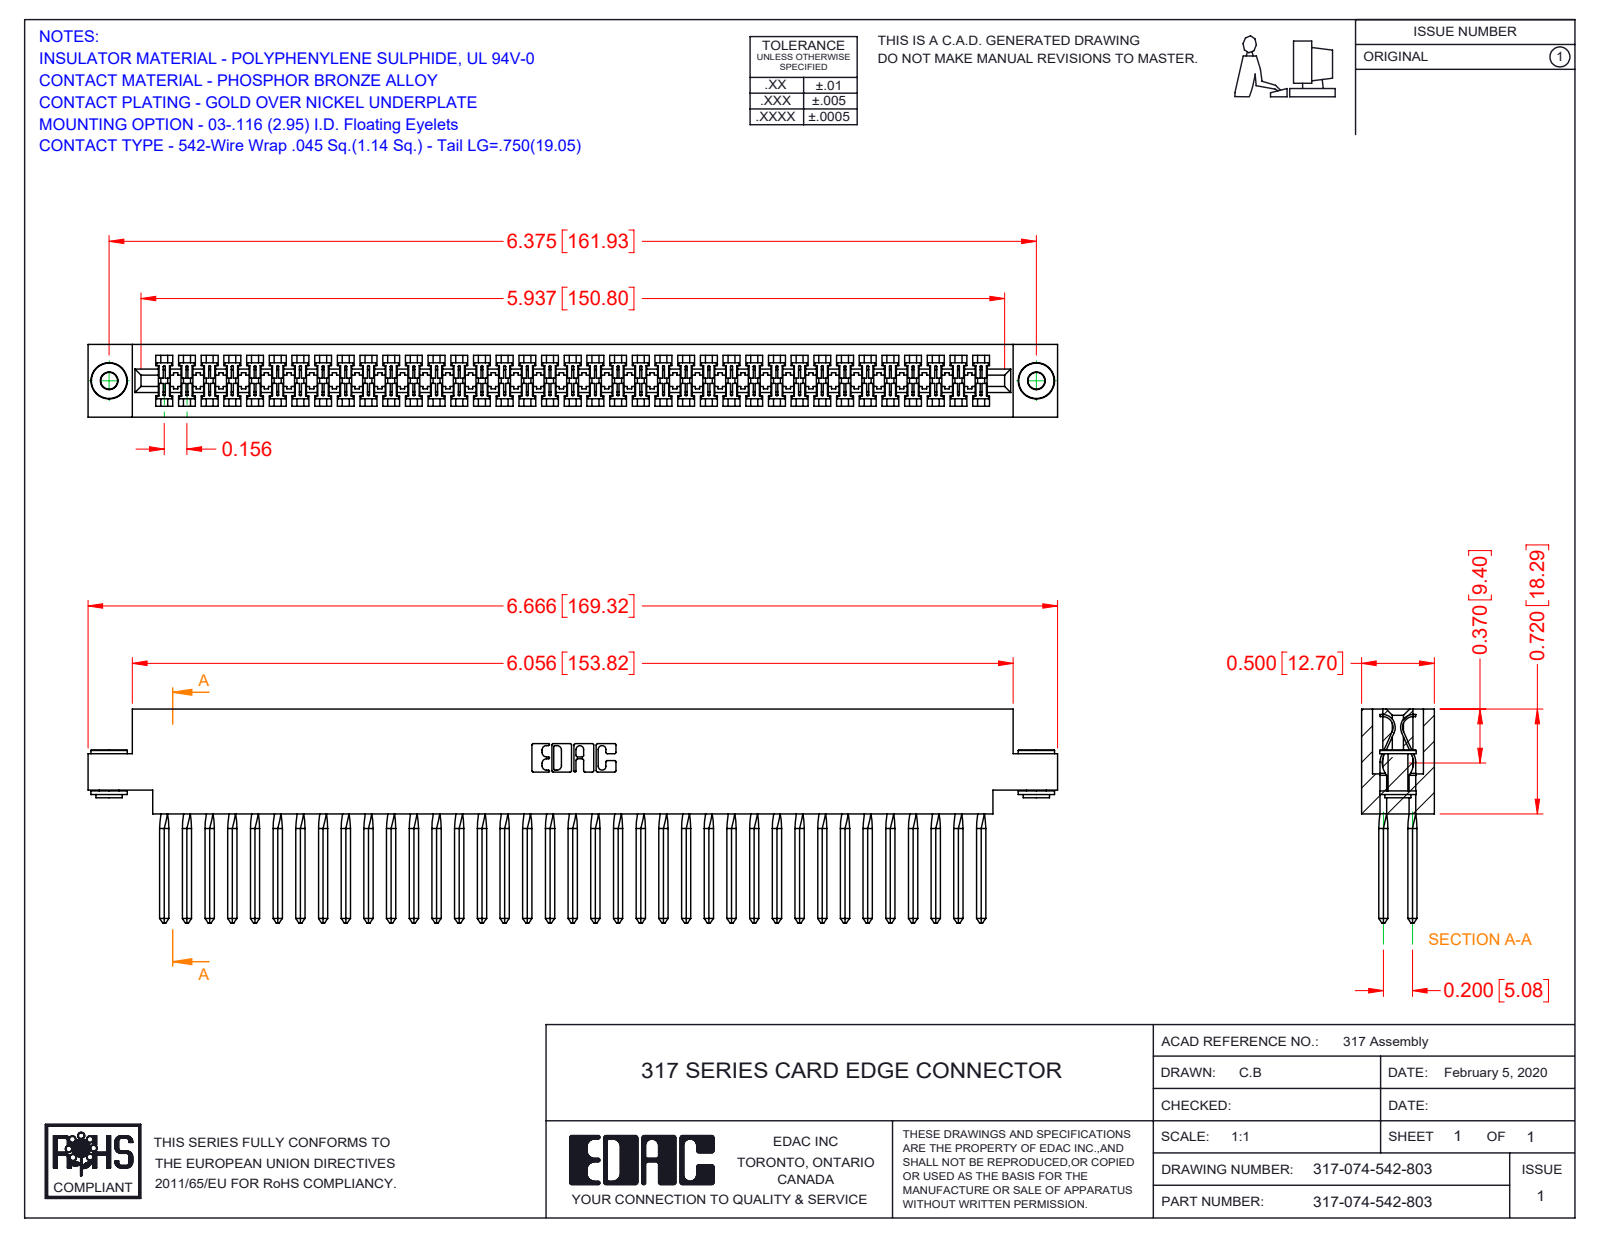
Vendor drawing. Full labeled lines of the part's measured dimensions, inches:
Part name (STEP PRODUCT): 317-074-542-803; 317-290-003_542; 317 Part_.156 Dia - TH; 345-250-002_345-250-002-102
STEP written by: SolidWorks 2016 (CONFIG_CONTROL_DESIGN)
Units: inches
Bodies: 77 solids, 4358 faces (3472 planar, 582 cylindrical, 304 other)
Overall size (bounding box): 6.666 × 1.47 × 0.5
Volume: 1.683 in³ · Surface area: 59.55 in²
Round holes (diameter × count): ⌀0.116 ×2, ⌀0.156 ×2
Round bosses / shafts (diameter × count): ⌀0.25 ×2, ⌀0.18 ×2, ⌀0.136 ×2
Partial cylindrical surfaces — rounded edges, fillets, slot ends (radius × count): R0.006 ×148, R0.01 ×22, R0.007 ×6, R0.031 ×6, R0.026 ×3, R0.074 ×2, R0.089 ×2, R0.1 ×2
Main face-to-face distances: 0.5, 0.075, 0.425, 0.35, 0.2, 0.046, 0.128, 0.372, 0.052, 0.297
Hole centre spacings: 6.375
